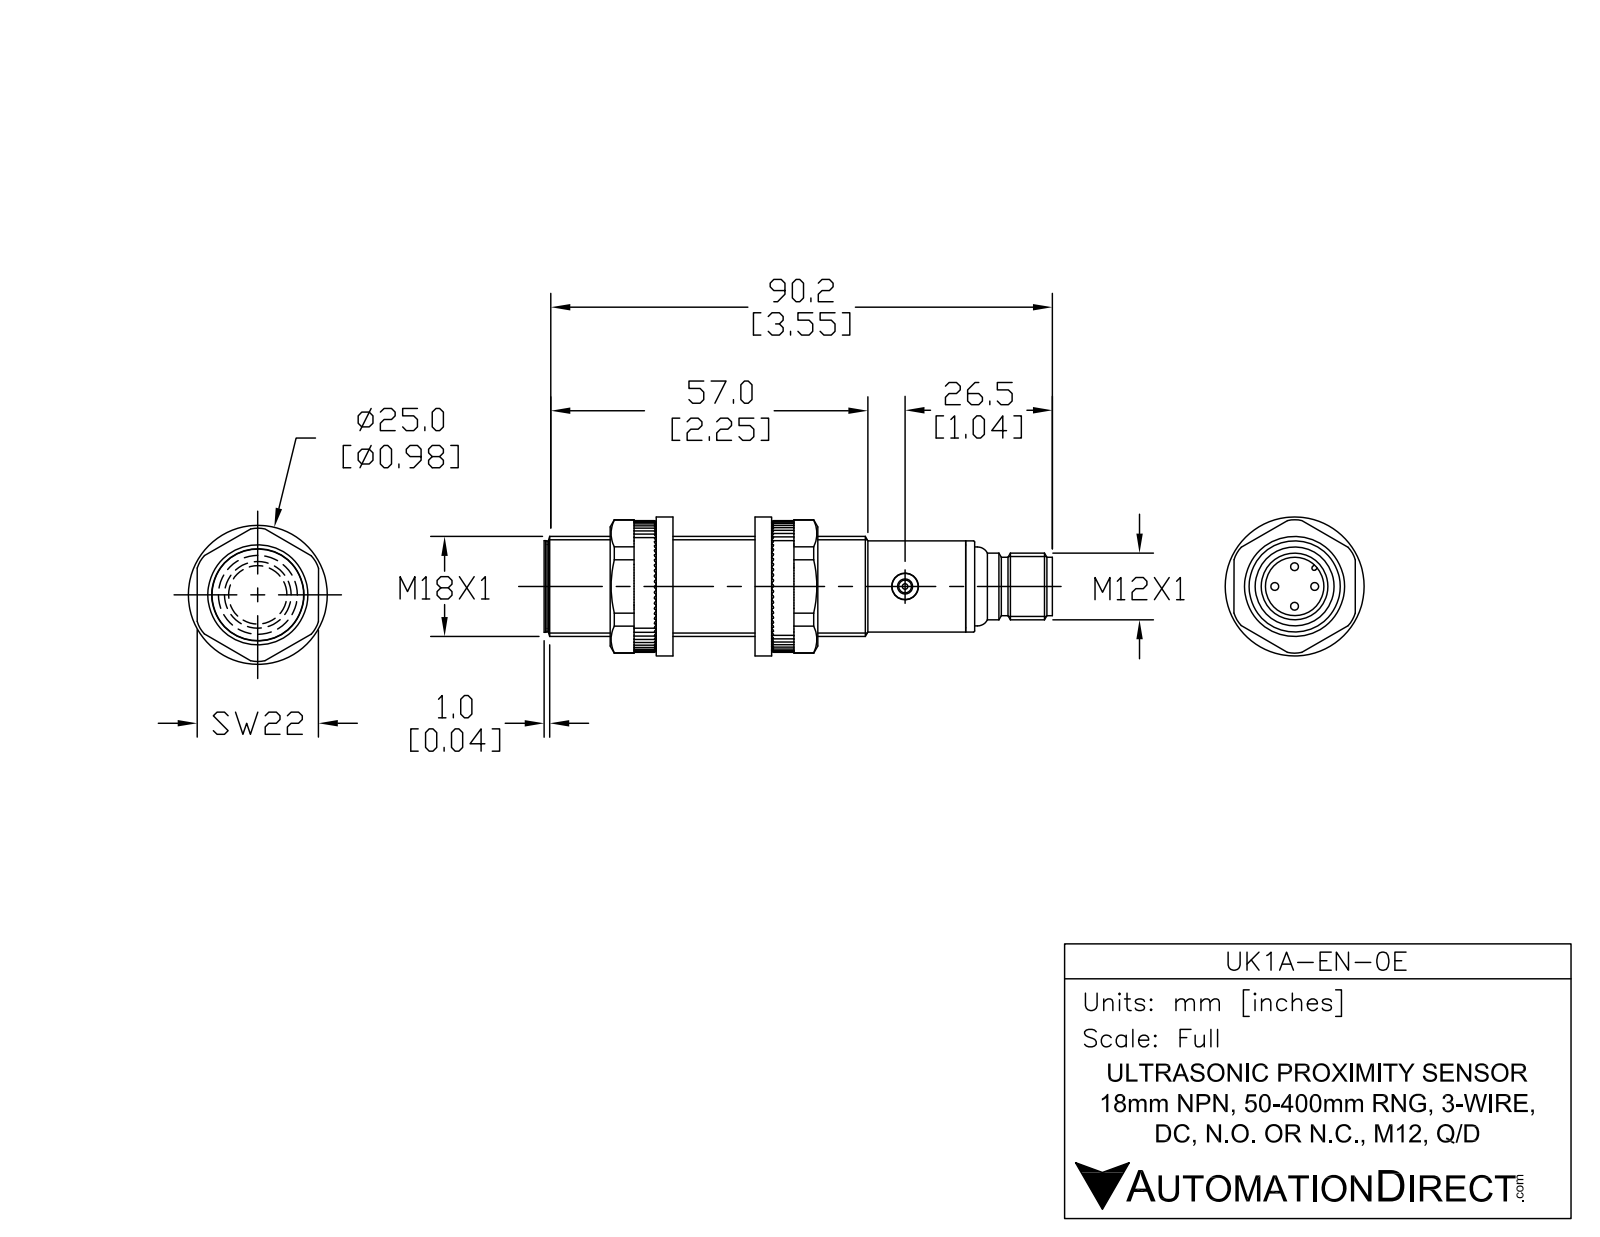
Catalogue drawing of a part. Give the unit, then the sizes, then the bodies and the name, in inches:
Units: inches
Overall size (bounding box): 3.606 × 0.709 × 0.709
Round holes (diameter × count): ⌀0.106 ×1, ⌀0.185 ×1, ⌀0.276 ×1, ⌀0.327 ×1, ⌀0.374 ×1
Round bosses / shafts (diameter × count): ⌀0.039 ×4, ⌀0.709 ×1, ⌀0.654 ×1, ⌀0.646 ×1, ⌀0.622 ×1, ⌀0.559 ×1, ⌀0.472 ×1, ⌀0.413 ×1
Partial cylindrical surfaces — rounded edges, fillets, slot ends (radius × count): R0.024 ×1
Main face-to-face distances: 2.957, 0.039, 2.996, 0.037, 2.994, 0.043, 0.157, 3.055, 3.053, 3.016
Volume: 1.202 in³ · Surface area: 10.68 in²
Bodies: 6 solids, 106 faces (21 planar, 48 cylindrical, 37 other)
Part name (STEP PRODUCT): UK1A-EN-0E
STEP written by: SolidWorks 2017 (AUTOMOTIVE_DESIGN)
